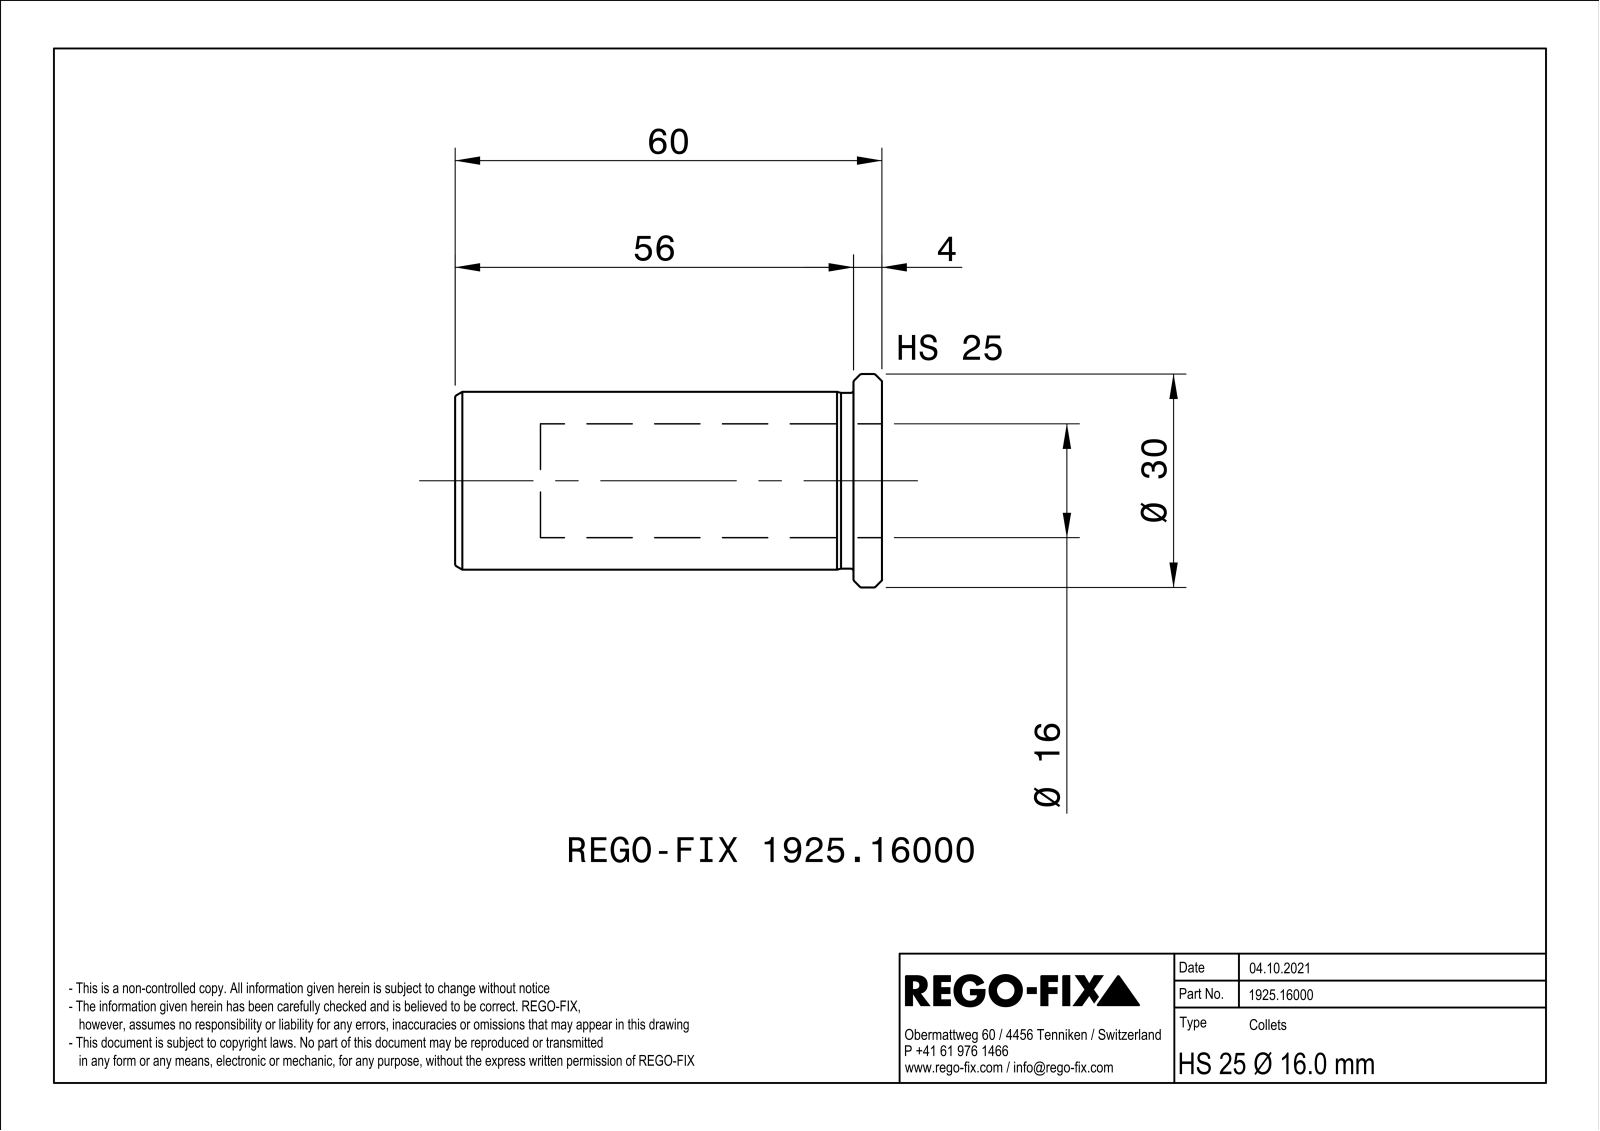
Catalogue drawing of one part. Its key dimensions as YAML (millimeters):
part_name: "NOCUT"
step_written_by: "SIEMENS PLM Software Solid Edge ST10 (AUTOMOTIVE_DESIGN)"
units: millimeters
bodies: {solids: 1, faces: 70, planar: 22, cylindrical: 11, other: 37}
overall_size: [60, 29.98, 29.98]
volume: 16028
surface_area: 9770
round_holes:
  - {diameter: 16, count: 1}
  - {diameter: 20.5, count: 1}
round_bosses_or_shafts:
  - {diameter: 30, count: 1}
  - {diameter: 25, count: 1}
  - {diameter: 24.7, count: 1}
face_to_face_distances: [1, 4, 60, 56]
